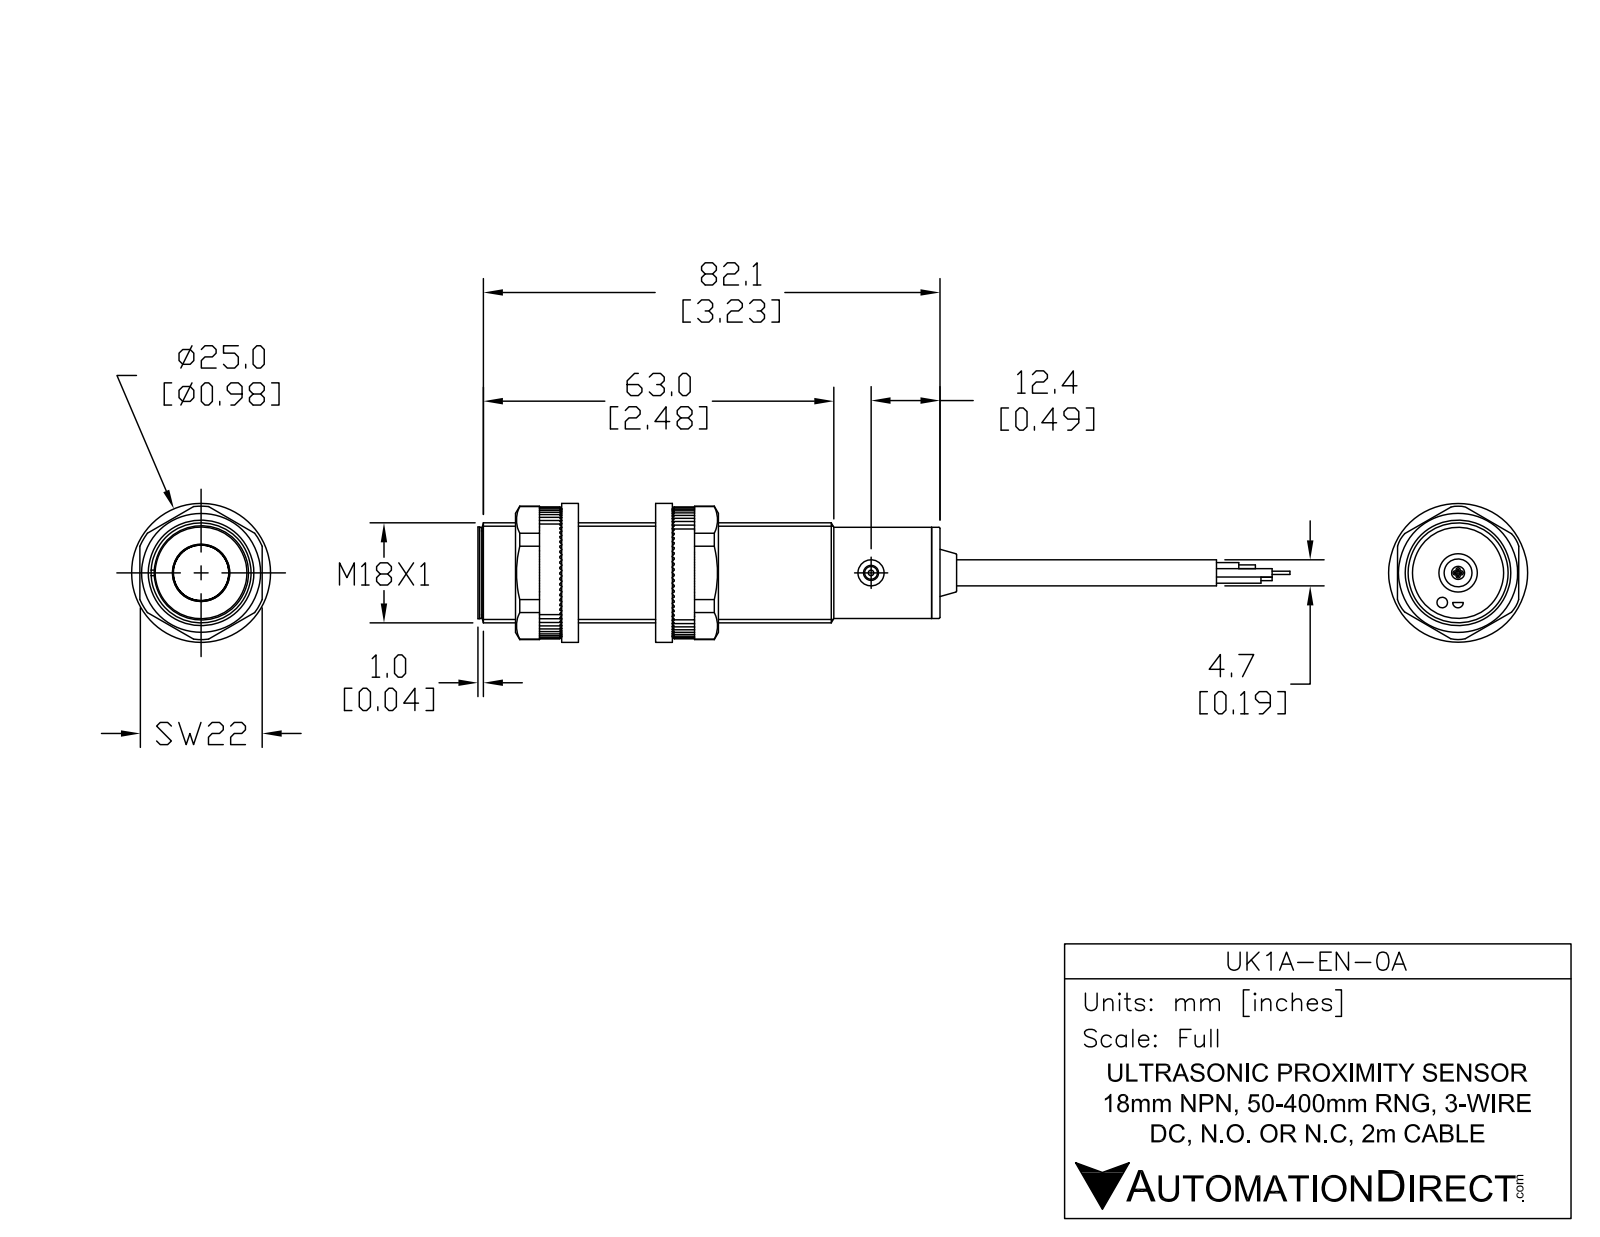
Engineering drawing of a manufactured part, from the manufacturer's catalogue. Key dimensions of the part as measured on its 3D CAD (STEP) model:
Part name (STEP PRODUCT): UK1A-EN-0A
STEP written by: SolidWorks 2017 (AUTOMOTIVE_DESIGN)
Units: inches
Bodies: 6 solids, 55 faces (17 planar, 24 cylindrical, 14 other)
Overall size (bounding box): 4.832 × 0.709 × 0.709
Volume: 1.285 in³ · Surface area: 10.69 in²
Round holes (diameter × count): ⌀0.185 ×2, ⌀0.106 ×1
Round bosses / shafts (diameter × count): ⌀0.709 ×1, ⌀0.646 ×1, ⌀0.622 ×1, ⌀0.374 ×1, ⌀0.189 ×1, ⌀0.091 ×1
Main face-to-face distances: 3.193, 3.252, 0.059, 0.039, 3.232, 3.291, 0.041, 3.234, 3.293, 3.257
